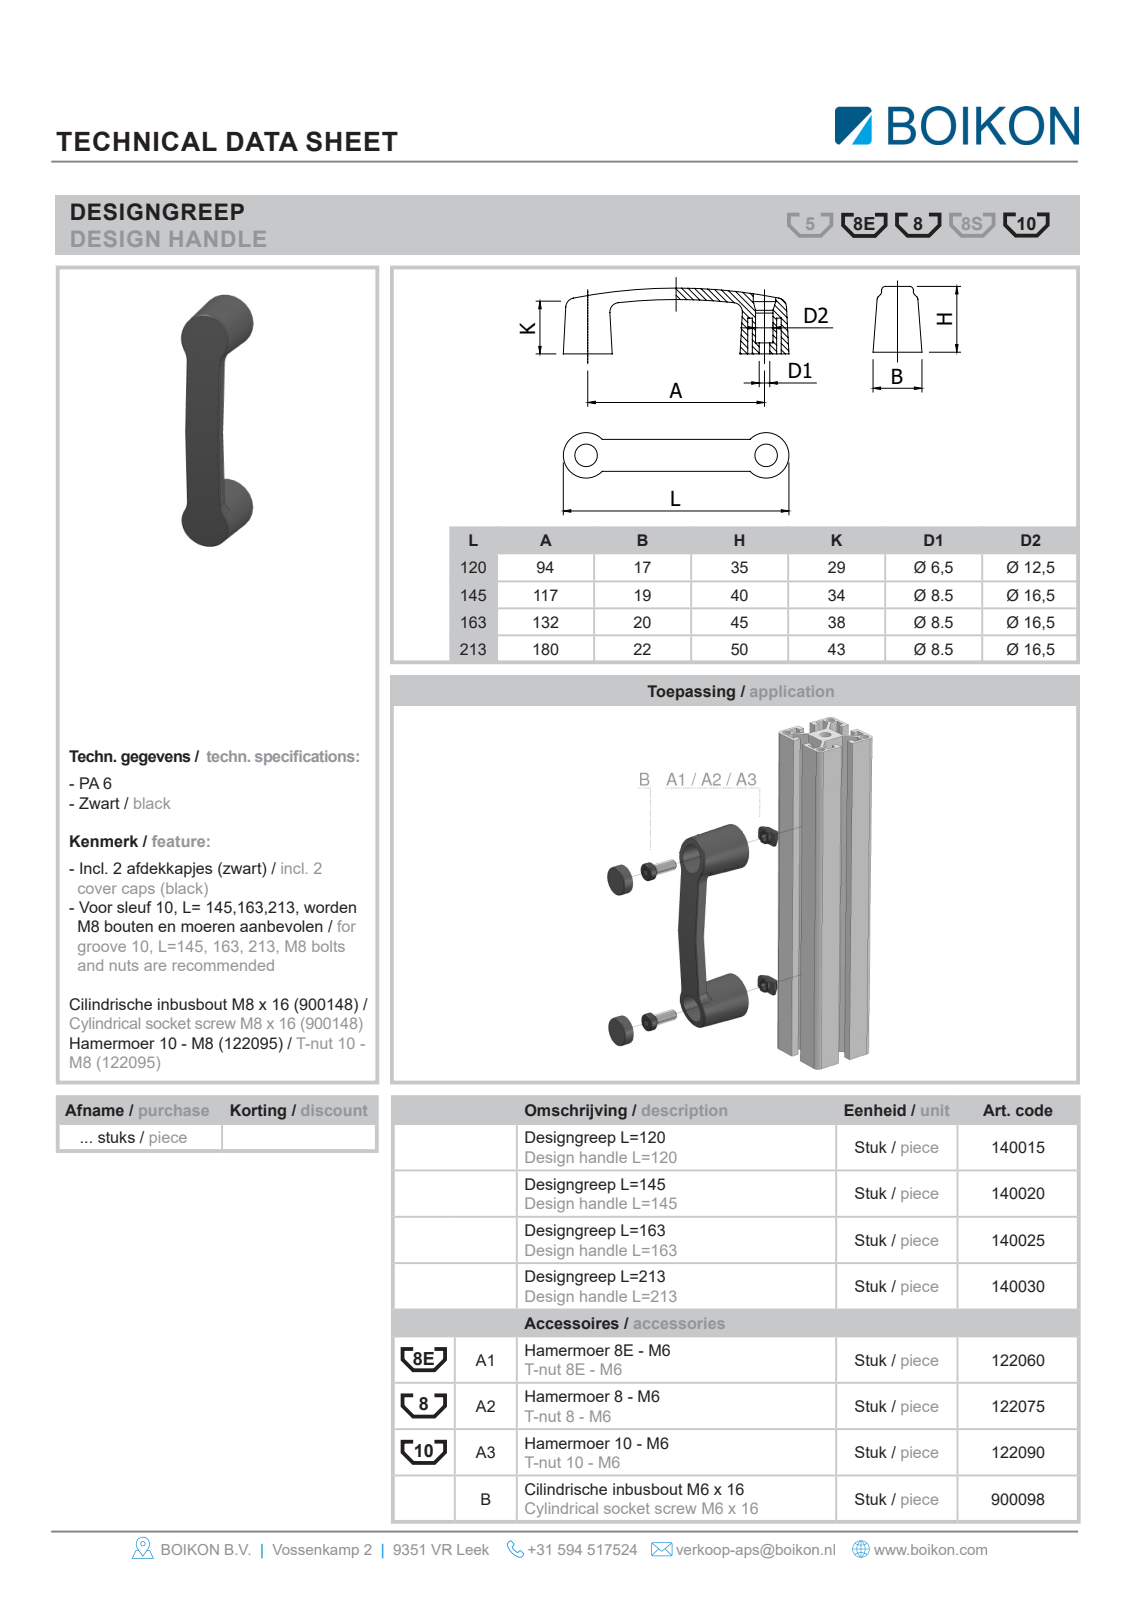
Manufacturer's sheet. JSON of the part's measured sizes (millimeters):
{"part_name": "Root; 140020Designgreep, L = 145BOIKON", "step_written_by": "HiCAD 2013 1802.4 Build 509 (AUTOMOTIVE_DESIGN)", "units": "millimeters", "bodies": {"solids": 1, "faces": 16, "planar": 8, "cylindrical": 2, "other": 6}, "overall_size": [146, 40, 29], "volume_mm3": 51310, "surface_area_mm2": 13513, "round_holes": [[8.5, 2]], "face_to_face_distances": [6, 34, 40, 19], "hole_center_spacings": [117]}
